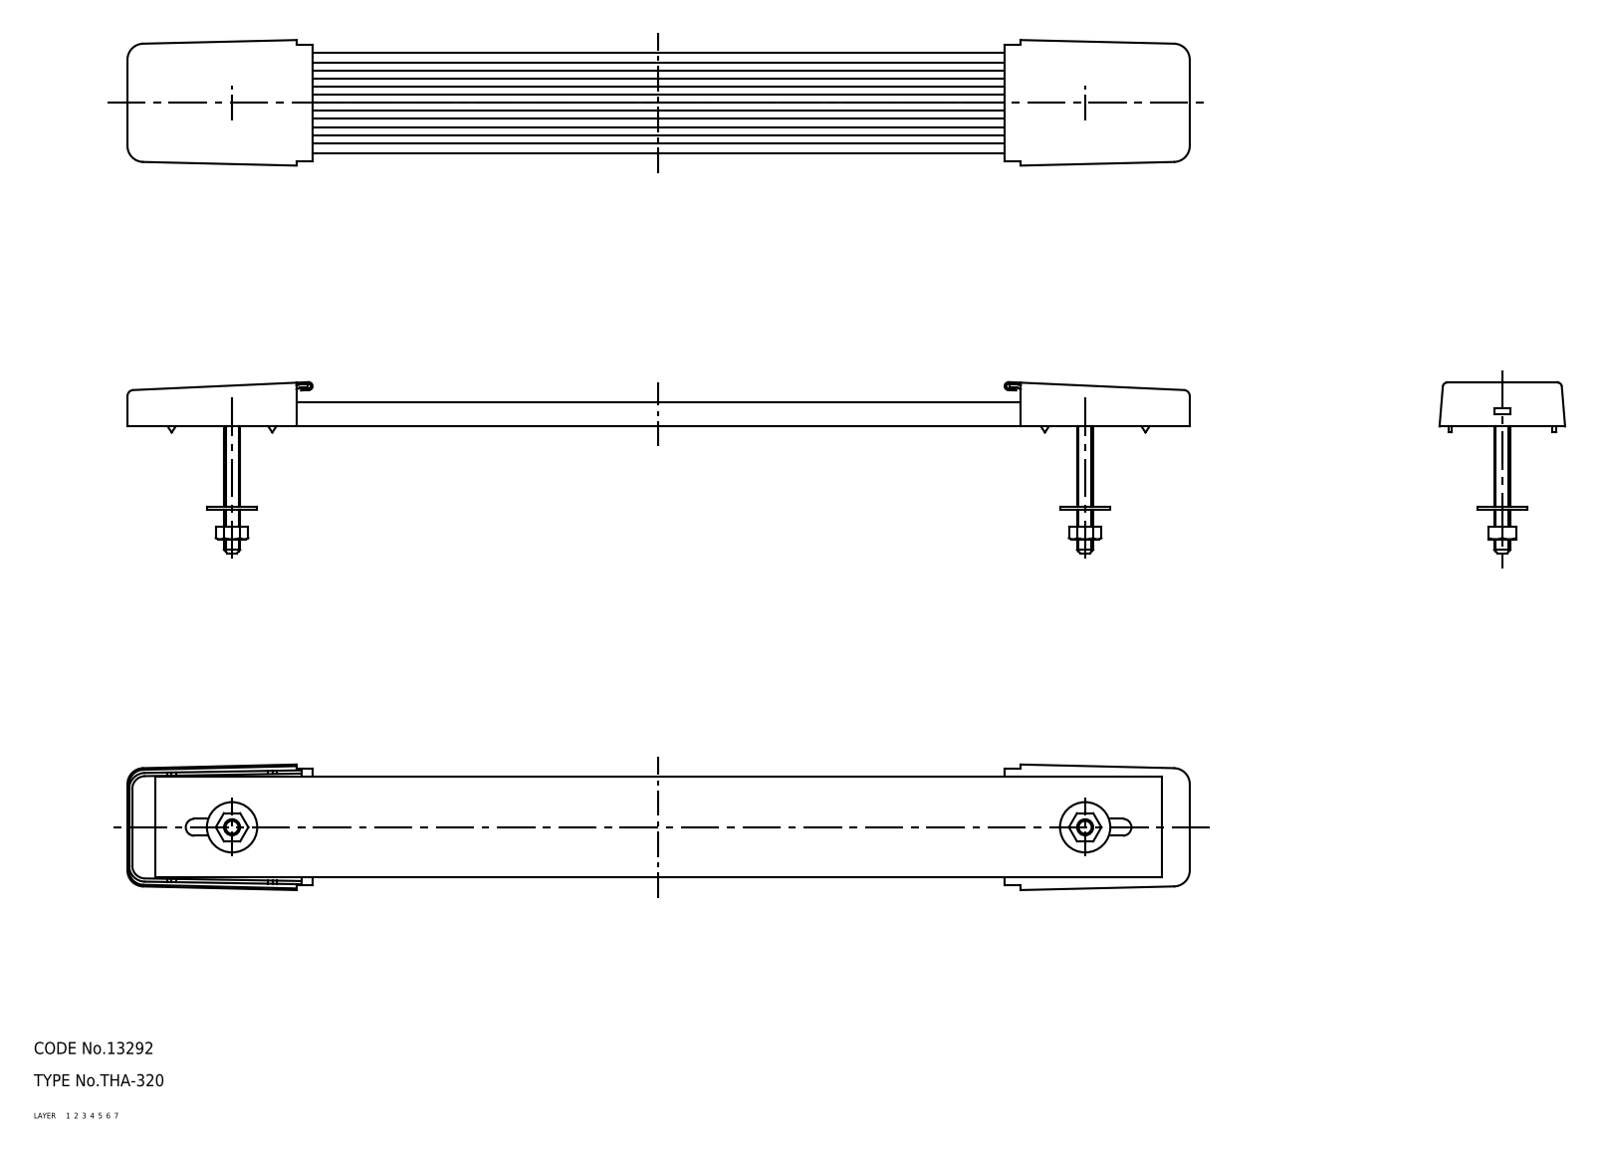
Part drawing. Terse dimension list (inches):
name: screw; washer; nut; bracket_B (+4 more)
written by: CADfix (AUTOMOTIVE_DESIGN)
unit: in
bodies: 12 solids, 314 faces (0 planar, 0 cylindrical, 314 other)
size: 10.394 × 1.673 × 1.228
volume: 2.53 in³; area: 83.48 in²
